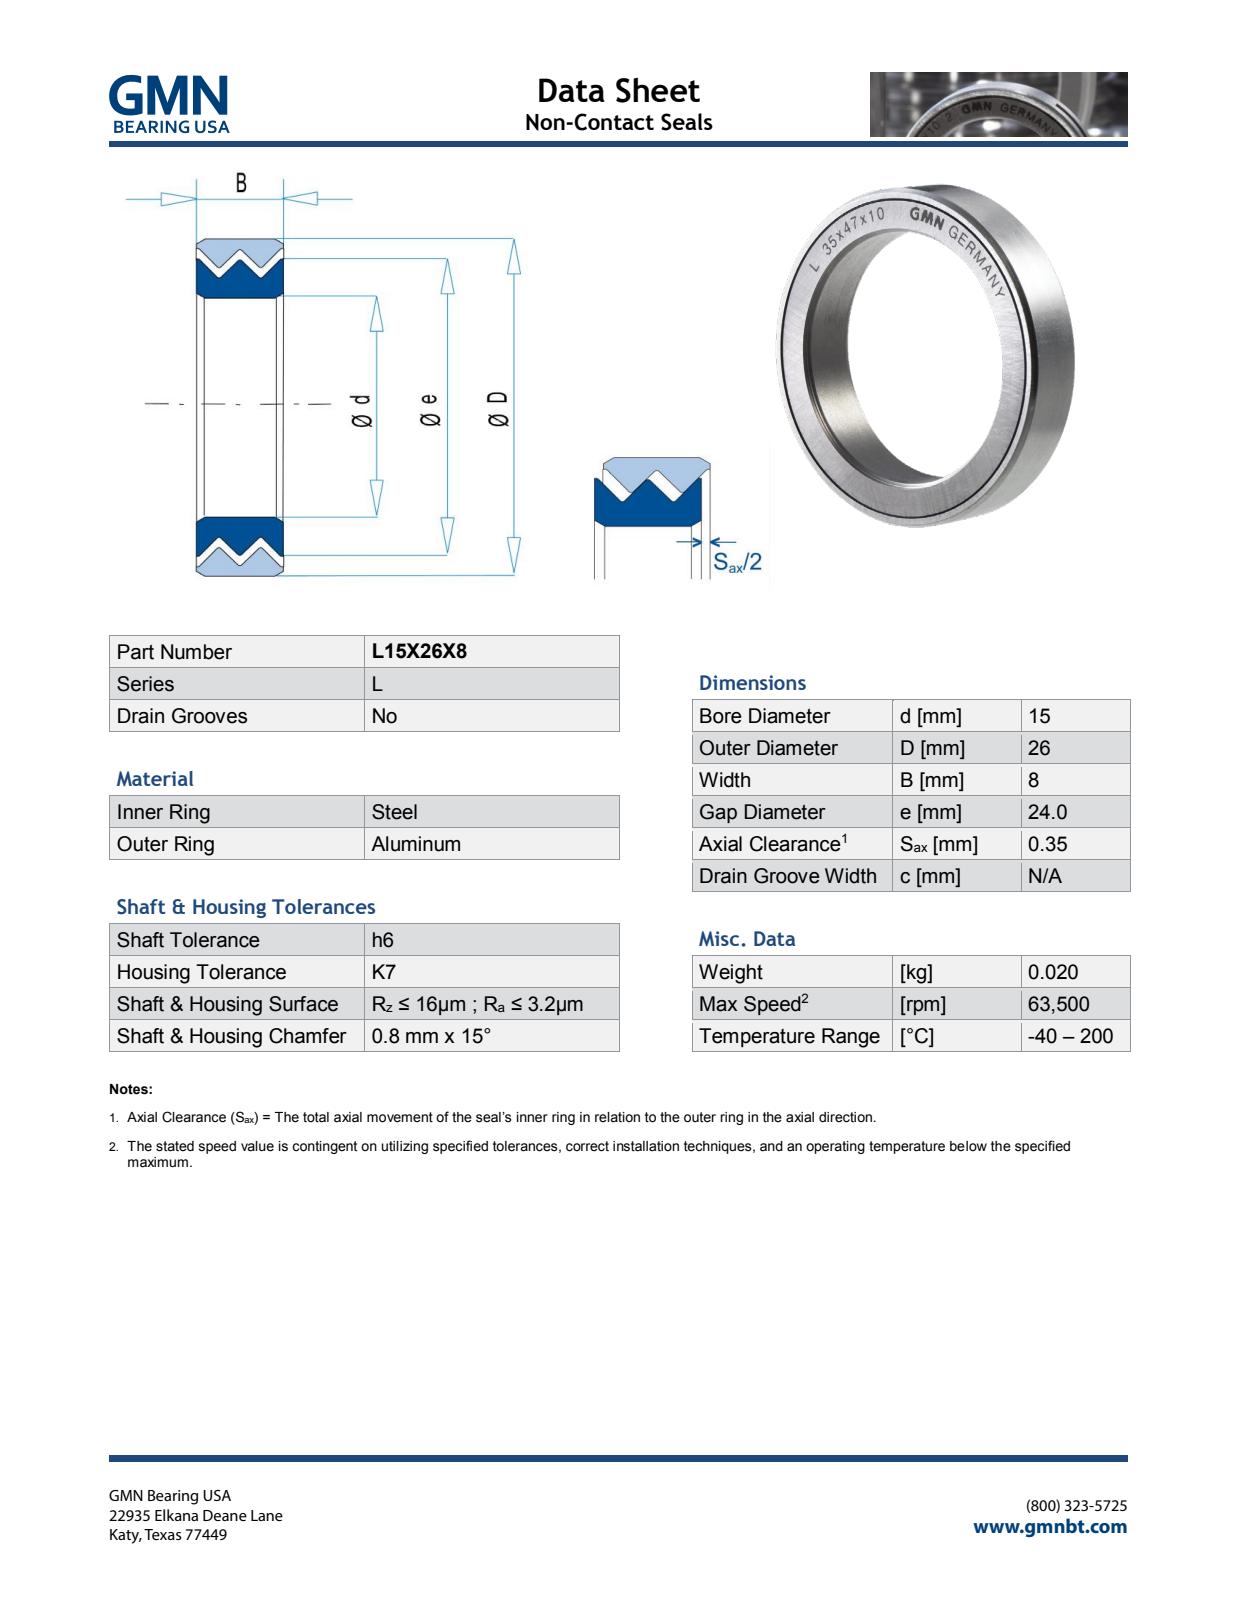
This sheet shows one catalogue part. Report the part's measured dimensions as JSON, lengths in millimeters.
{"part_name": "L15X26X8_PRT", "step_written_by": "PRO/ENGINEER BY PARAMETRIC TECHNOLOGY CORPORATION, 2013150 (AUTOMOTIVE_DESIGN)", "units": "millimeters", "bodies": {"solids": 2, "faces": 576, "planar": 520, "cylindrical": 12, "other": 44}, "overall_size": [26, 26, 8.07], "volume_mm3": 2664, "surface_area_mm2": 3236, "round_holes": [[15, 1], [24.24, 1]], "round_bosses_or_shafts": [[26, 1], [24, 1]], "face_to_face_distances": [8, 8.07, 1.92, 1.68, 1.36, 1.44, 0.86, 1.93, 1.6, 1.12]}
